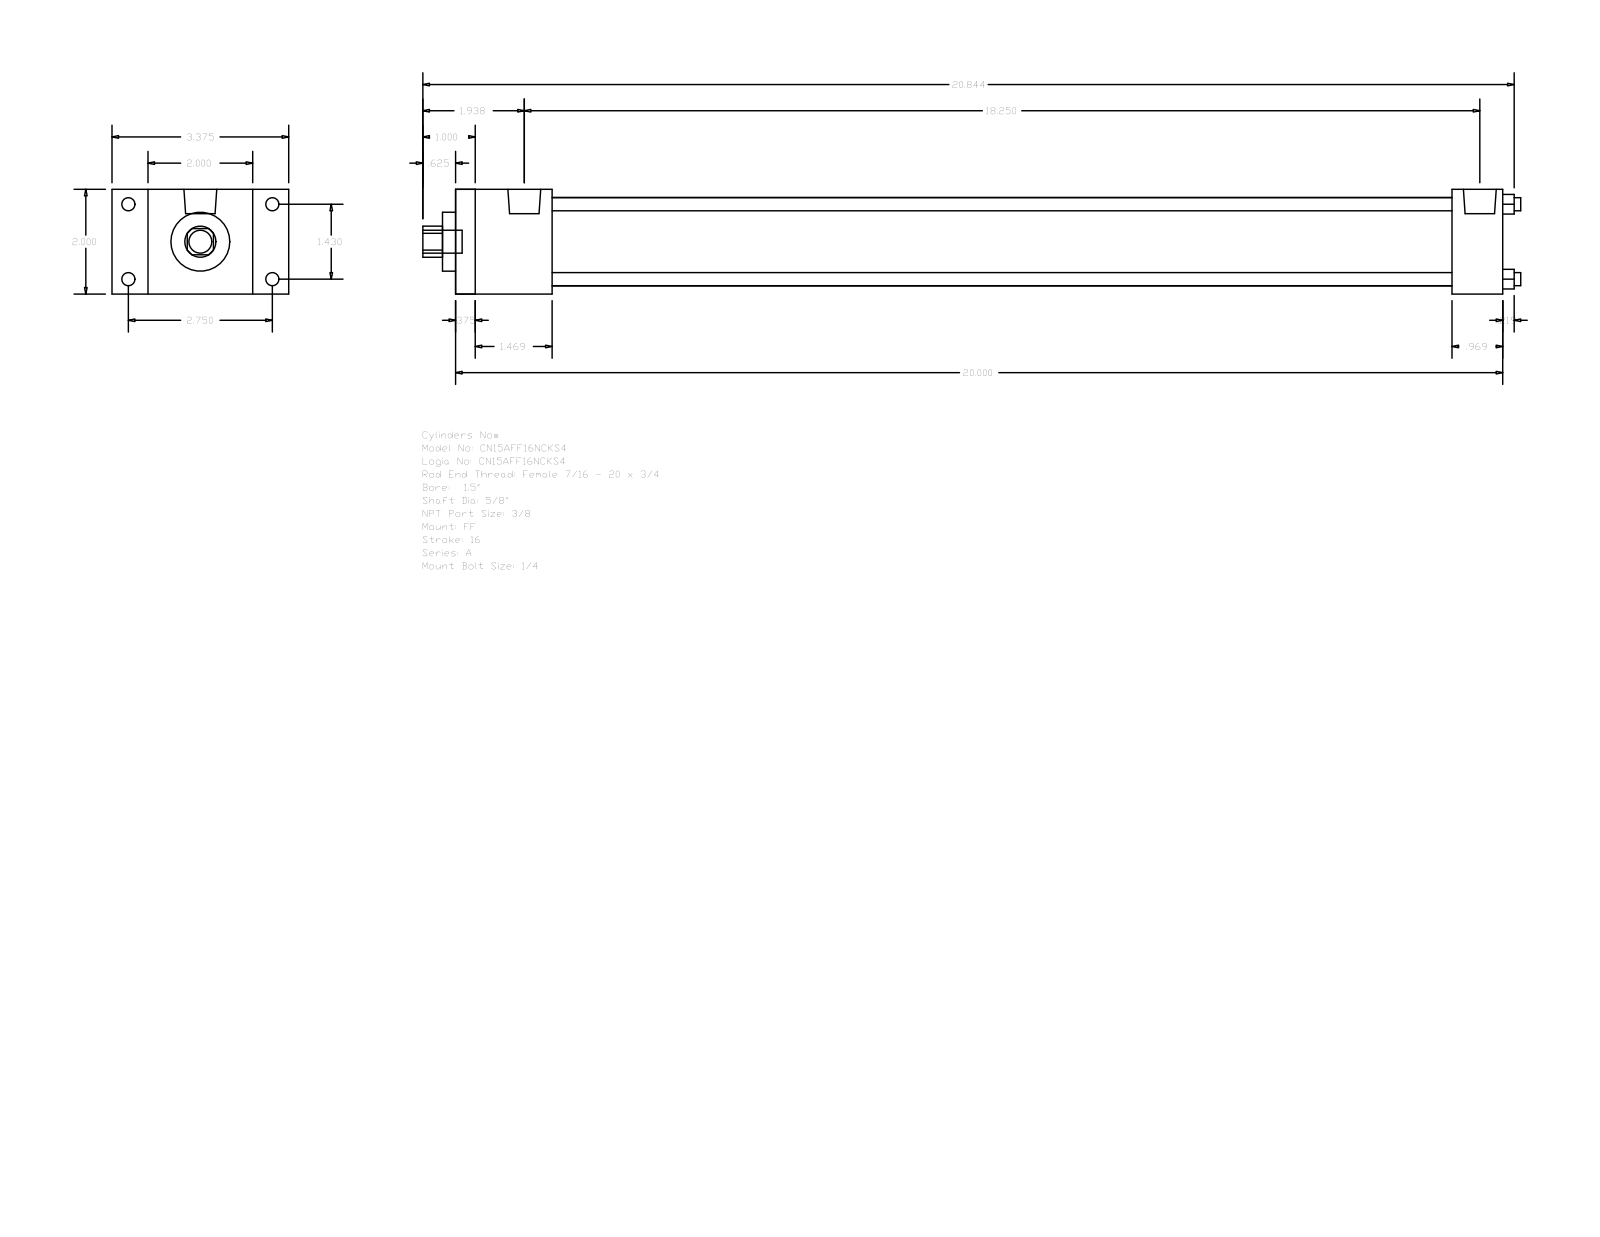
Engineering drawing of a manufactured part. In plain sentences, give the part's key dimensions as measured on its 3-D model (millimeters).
The part is named "A_FF__0150_0.625". Its 3-D file was written by "GSSL Pune (CONFIG_CONTROL_DESIGN)". It is 0 solids with 92 faces: 64 planar, 28 cylindrical and 0 other. Overall it measures 532.61 by 85.72 by 50.8 millimeters. Round holes: 4 of diameter 6.35, 1 of diameter 15.88, 1 of diameter 28.57, 1 of diameter 42.93. Round bosses or shafts: 4 of diameter 6.35, 4 of diameter 5.56, 2 of diameter 15.93, 1 of diameter 11.11. Partial cylindrical surfaces (rounded edges, fillets, slot ends): 1 of radius 7.54. The main face-to-face distances are 50.8, 508, 9.52, 498.48, 46.83, 483.39, 37.31, 473.87, 436.56, 461.17. The hole center spacings are 25.68, 36.32, 51.36.
